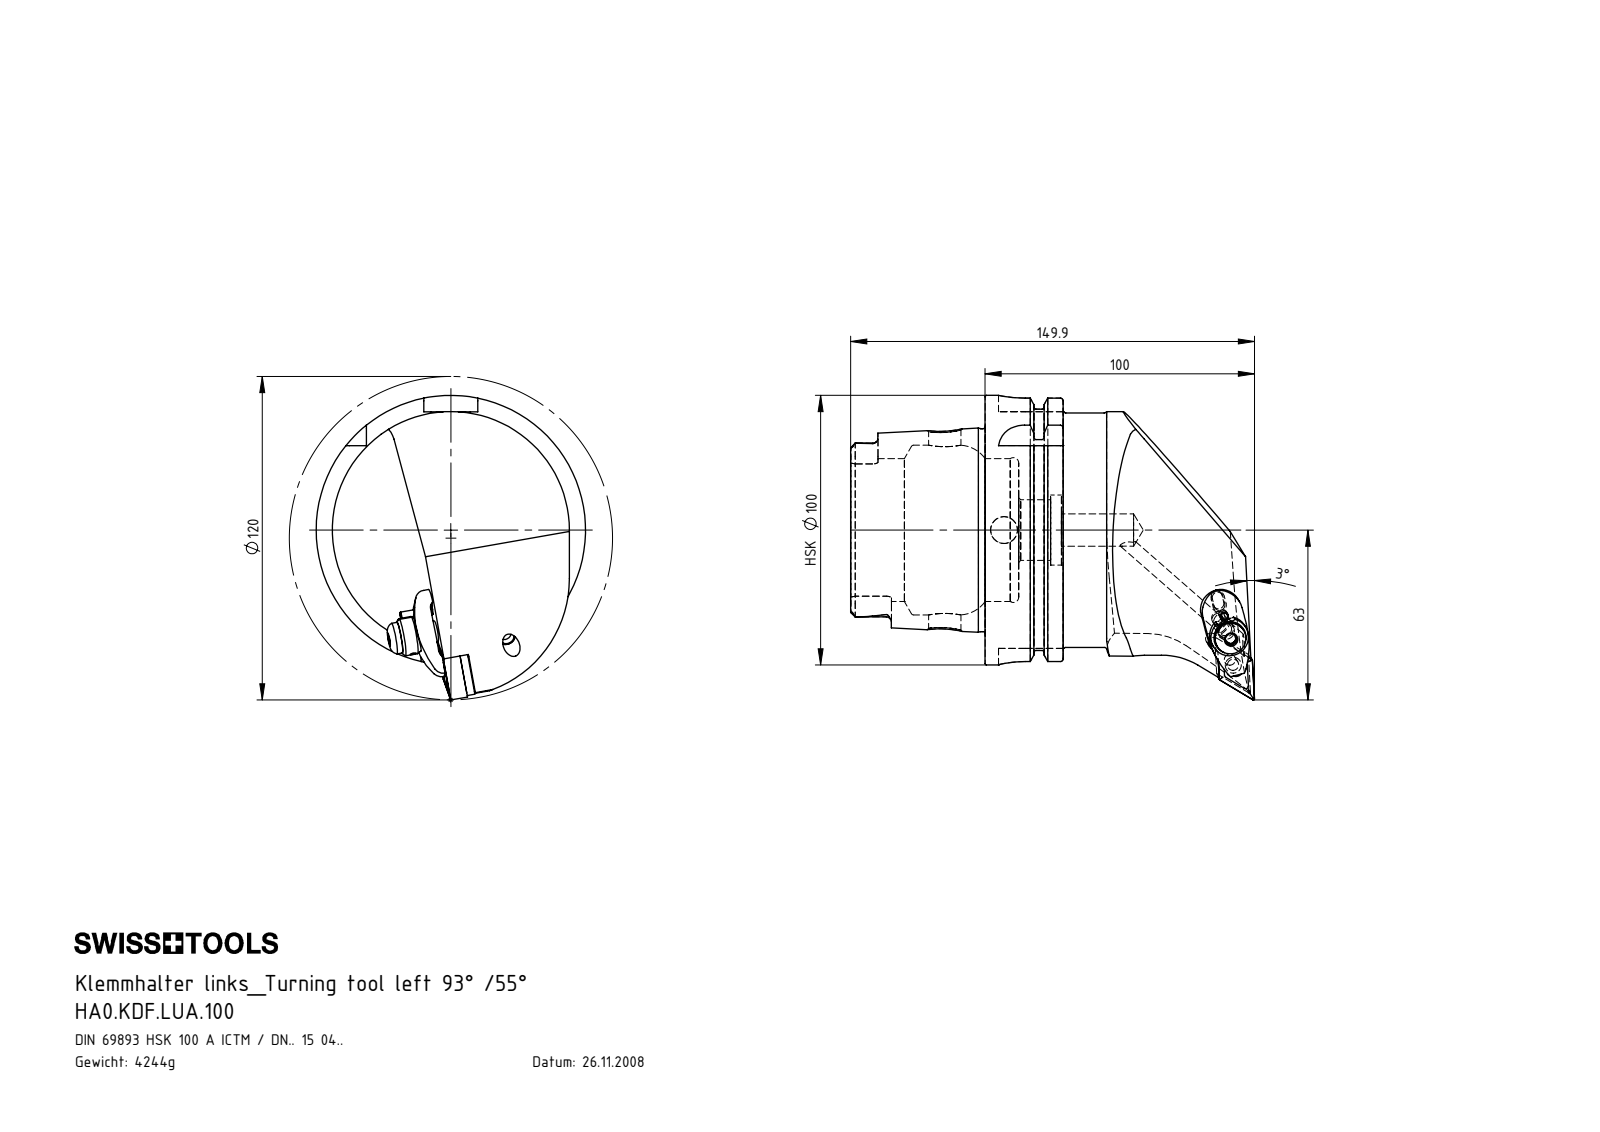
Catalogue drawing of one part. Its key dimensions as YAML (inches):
part_name: "HA0.KDF.LUA.100; WDF-ER2.101.003_A; ISO 13337 - 3 x 12_PreviewCfg; WCC-ER4.103.032_A (+7 more)"
step_written_by: "SolidWorks 2017 (AUTOMOTIVE_DESIGN)"
units: inches
bodies: {solids: 11, faces: 466, planar: 122, cylindrical: 153, other: 191}
overall_size: [5.902, 4.449, 3.937]
volume: 33.05
surface_area: 113.6
round_holes:
  - {diameter: 0.079, count: 3}
  - {diameter: 0.197, count: 3}
  - {diameter: 0.276, count: 2}
  - {diameter: 0.472, count: 2}
  - {diameter: 0.094, count: 1}
  - {diameter: 0.118, count: 1}
  - {diameter: 0.165, count: 1}
  - {diameter: 0.203, count: 1}
  - {diameter: 0.236, count: 1}
  - {diameter: 0.244, count: 1}
  - {diameter: 0.256, count: 1}
  - {diameter: 0.335, count: 1}
round_bosses_or_shafts:
  - {diameter: 0.236, count: 2}
  - {diameter: 0.118, count: 2}
  - {diameter: 3.937, count: 1}
  - {diameter: 3.62, count: 1}
  - {diameter: 3.425, count: 1}
  - {diameter: 2.963, count: 1}
  - {diameter: 0.551, count: 1}
  - {diameter: 0.453, count: 1}
partial_cylinders:
  - {radius: 0.015, count: 6}
  - {radius: 0.027, count: 6}
  - {radius: 0.075, count: 6}
  - {radius: 0.016, count: 4}
  - {radius: 0.394, count: 4}
  - {radius: 0.059, count: 3}
  - {radius: 0.079, count: 2}
  - {radius: 0.118, count: 2}
face_to_face_distances: [0.49, 0.65, 1.14, 1.965, 2.455, 3.104, 3.457, 3.079, 1.114, 0.624]
hole_center_spacings: [0.591, 0.315, 0.315, 0.583, 0.906, 0.322, 0.323, 0.591]
